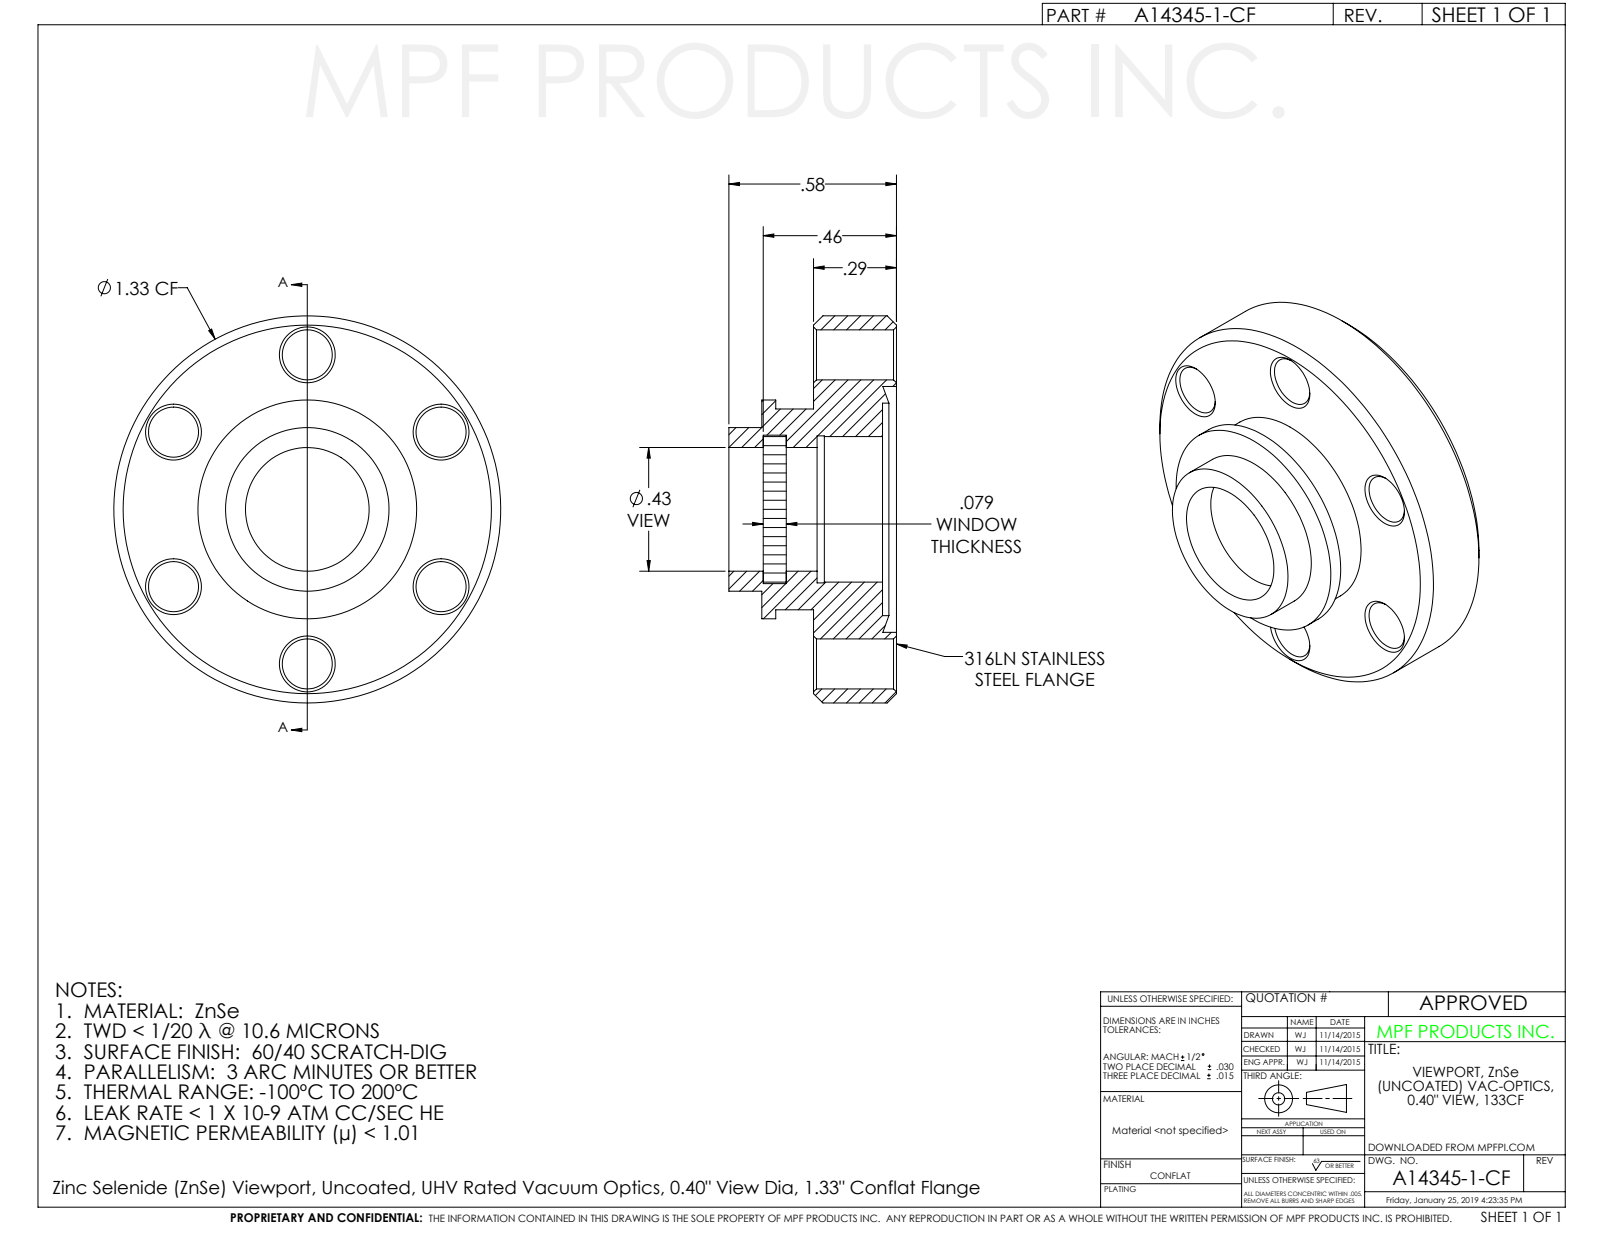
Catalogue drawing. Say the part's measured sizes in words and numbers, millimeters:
The part is named "A14345-1-CF". Its 3-D file was written by "SolidWorks 2014 (CONFIG_CONTROL_DESIGN)". It is 1 solid with 81 faces: 13 planar, 38 cylindrical and 30 other. Overall it measures 33.8 by 33.8 by 14.6 millimeters. Its volume is 5 650 cubic millimeters and its surface area 4 101 square millimeters. Round holes: 6 of diameter 4.4, 1 of diameter 10.8, 1 of diameter 10.8, 1 of diameter 12.7, 1 of diameter 17.8, 1 of diameter 18.5, 1 of diameter 19.7, 1 of diameter 21.5. Round bosses or shafts: 1 of diameter 33.8, 1 of diameter 19.1, 1 of diameter 19.1, 1 of diameter 17.5, 1 of diameter 15.2, 1 of diameter 14.3. The main face-to-face distances are 7.2, 11.7, 4.5, 1.2, 10.5, 11.6, 4.4, 9.1, 1.8, 2.5. The hole center spacings are 13.5, 23.4, 13.5, 27, 27.
